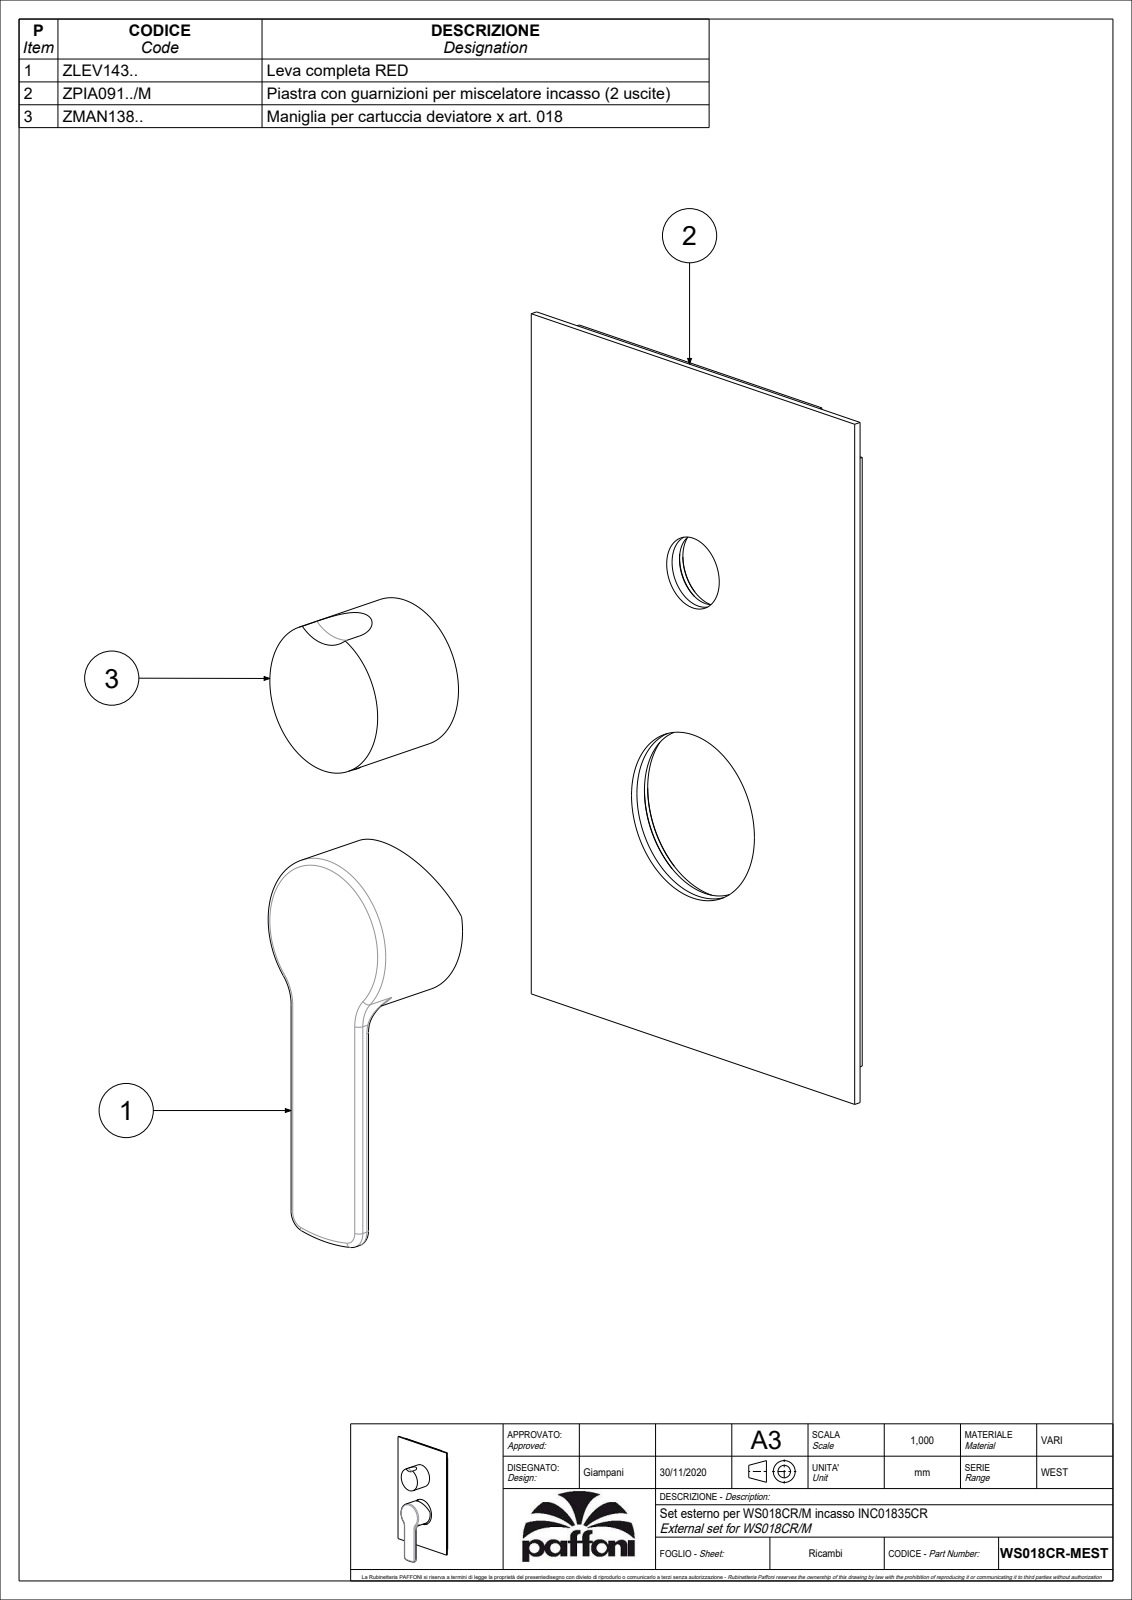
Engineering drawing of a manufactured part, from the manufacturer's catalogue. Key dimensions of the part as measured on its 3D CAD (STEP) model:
Part name (STEP PRODUCT): WS018CR-MEST
STEP written by: CREO PARAMETRIC BY PTC INC, 2020044 (CONFIG_CONTROL_DESIGN)
Units: millimetres
Bodies: 3 solids, 360 faces (118 planar, 126 cylindrical, 116 other)
Overall size (bounding box): 209 × 120 × 39.85
Volume: 96 401 mm³ · Surface area: 73 779 mm²
Round holes (diameter × count): ⌀3 ×2, ⌀3.2 ×1, ⌀3.3 ×1, ⌀4.2 ×1, ⌀4.5 ×1, ⌀14.8 ×1, ⌀19.5 ×1, ⌀21.5 ×1, ⌀25 ×1, ⌀36 ×1, ⌀45.6 ×1, ⌀47.6 ×1
Round bosses / shafts (diameter × count): ⌀7.6 ×2, ⌀5.5 ×2, ⌀54.6 ×1, ⌀43 ×1, ⌀40 ×1, ⌀28.5 ×1, ⌀24 ×1, ⌀5 ×1
Partial cylindrical surfaces — rounded edges, fillets, slot ends (radius × count): R0.5 ×39, R1.5 ×4, R5 ×2, R10 ×2, R12.5 ×1, R50 ×1
Main face-to-face distances: 2, 0.8, 2.8, 30.3, 29.5, 27.5, 34, 32, 4.5, 34.8
Hole centre spacings: 6, 10, 68, 78
